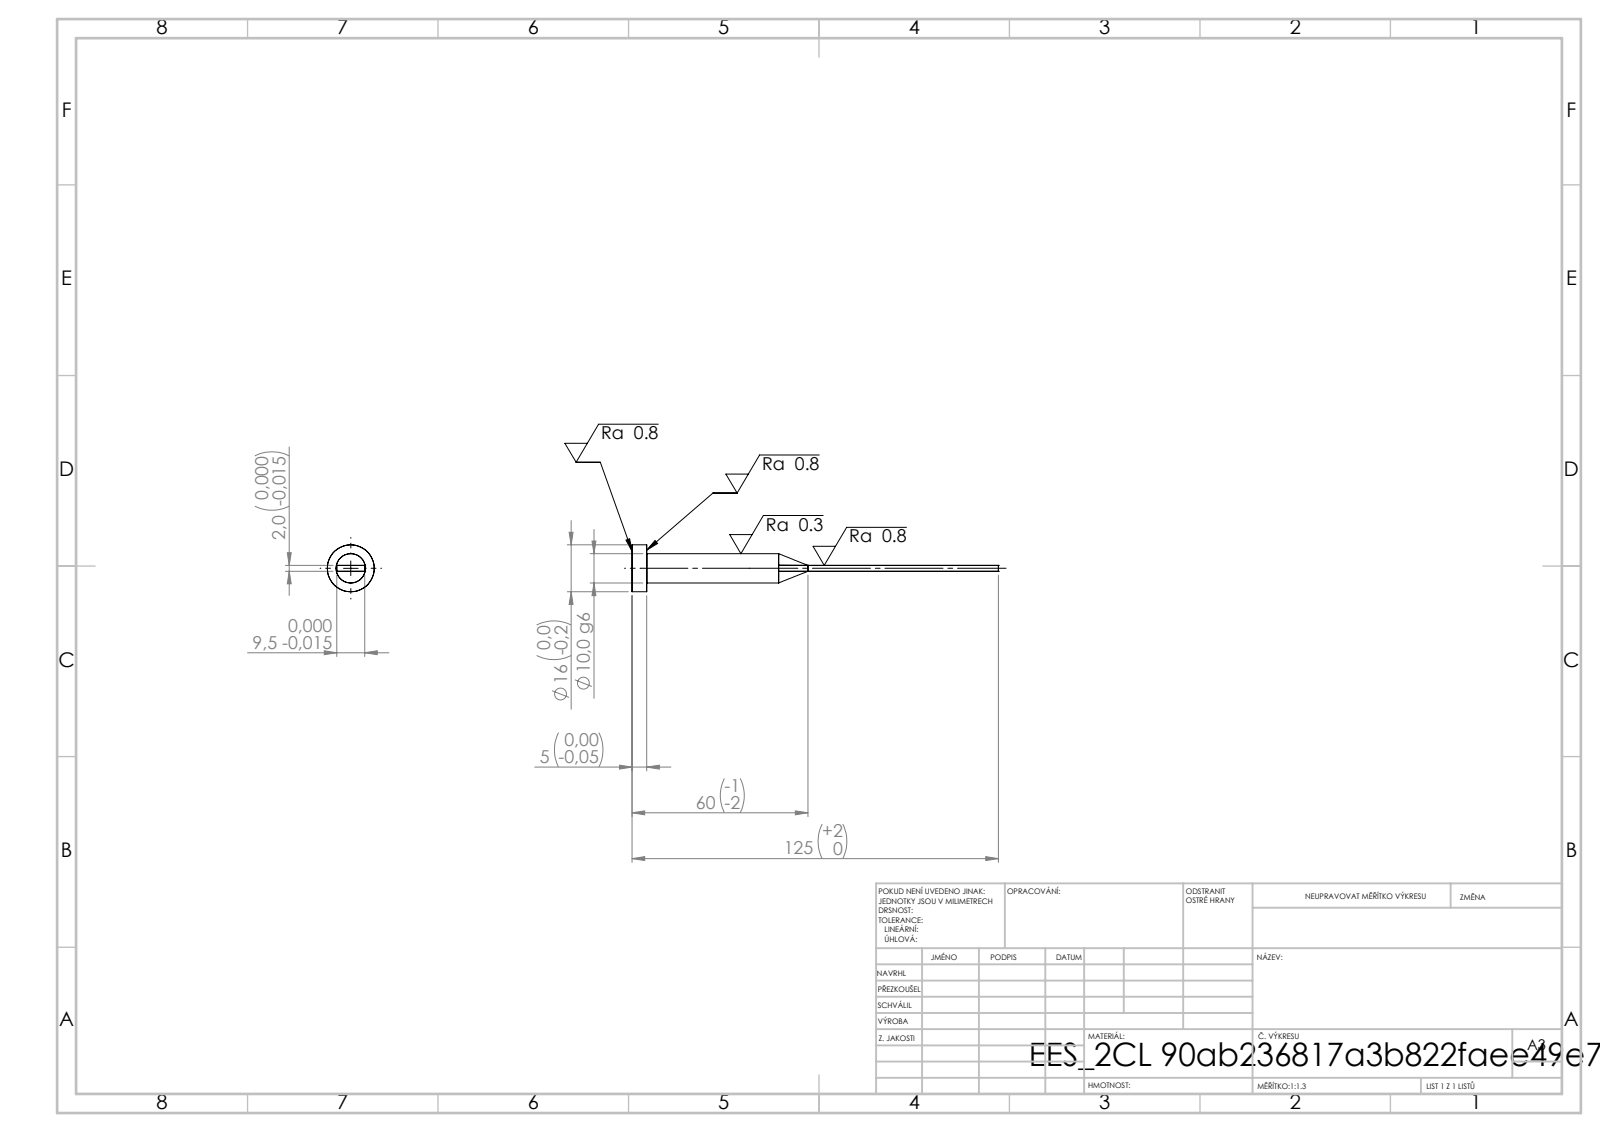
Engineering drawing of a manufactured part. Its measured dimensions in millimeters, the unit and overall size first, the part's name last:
Units: millimetres
Overall size (bounding box): 125 × 16 × 16
Round bosses / shafts (diameter × count): ⌀16 ×1, ⌀10 ×1
Main face-to-face distances: 2, 9.5, 5, 125, 120
Volume: 6 240 mm³ · Surface area: 3 772 mm²
Bodies: 1 solid, 15 faces (7 planar, 4 cylindrical, 4 other)
STEP written by: SolidWorks 2019 (CONFIG_CONTROL_DESIGN)
